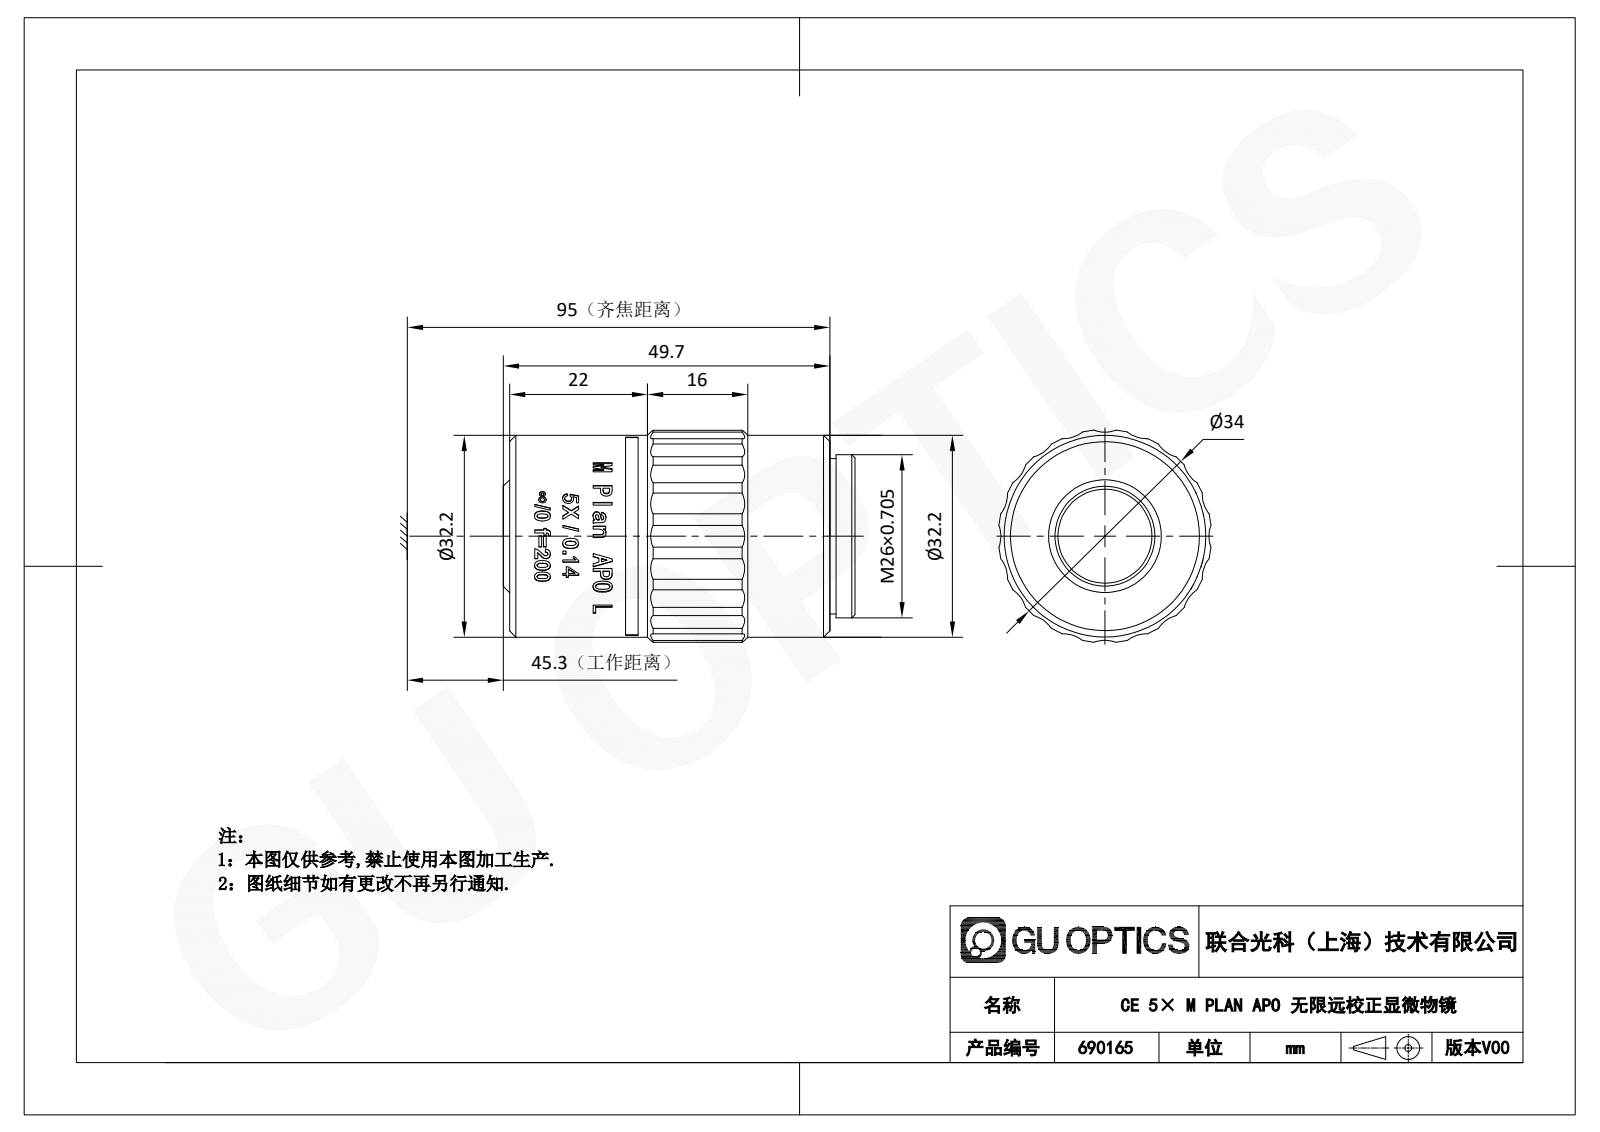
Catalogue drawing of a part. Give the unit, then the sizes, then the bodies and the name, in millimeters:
Units: millimetres
Overall size (bounding box): 54.7 × 33.82 × 33.82
Round holes (diameter × count): ⌀15 ×1, ⌀22 ×1
Round bosses / shafts (diameter × count): ⌀32.2 ×1, ⌀32 ×1, ⌀26 ×1, ⌀24.8 ×1
Partial cylindrical surfaces — rounded edges, fillets, slot ends (radius × count): R5 ×20, R15.9 ×1, R17 ×1
Main face-to-face distances: 51, 49.7, 1.3, 0.5, 51.5, 50.2, 4, 2.7, 53.7, 54.2
Volume: 42 669 mm³ · Surface area: 7 385 mm²
Bodies: 1 solid, 378 faces (121 planar, 94 cylindrical, 163 other)
Part name (STEP PRODUCT): 690164
STEP written by: SolidWorks 2020 (CONFIG_CONTROL_DESIGN)
